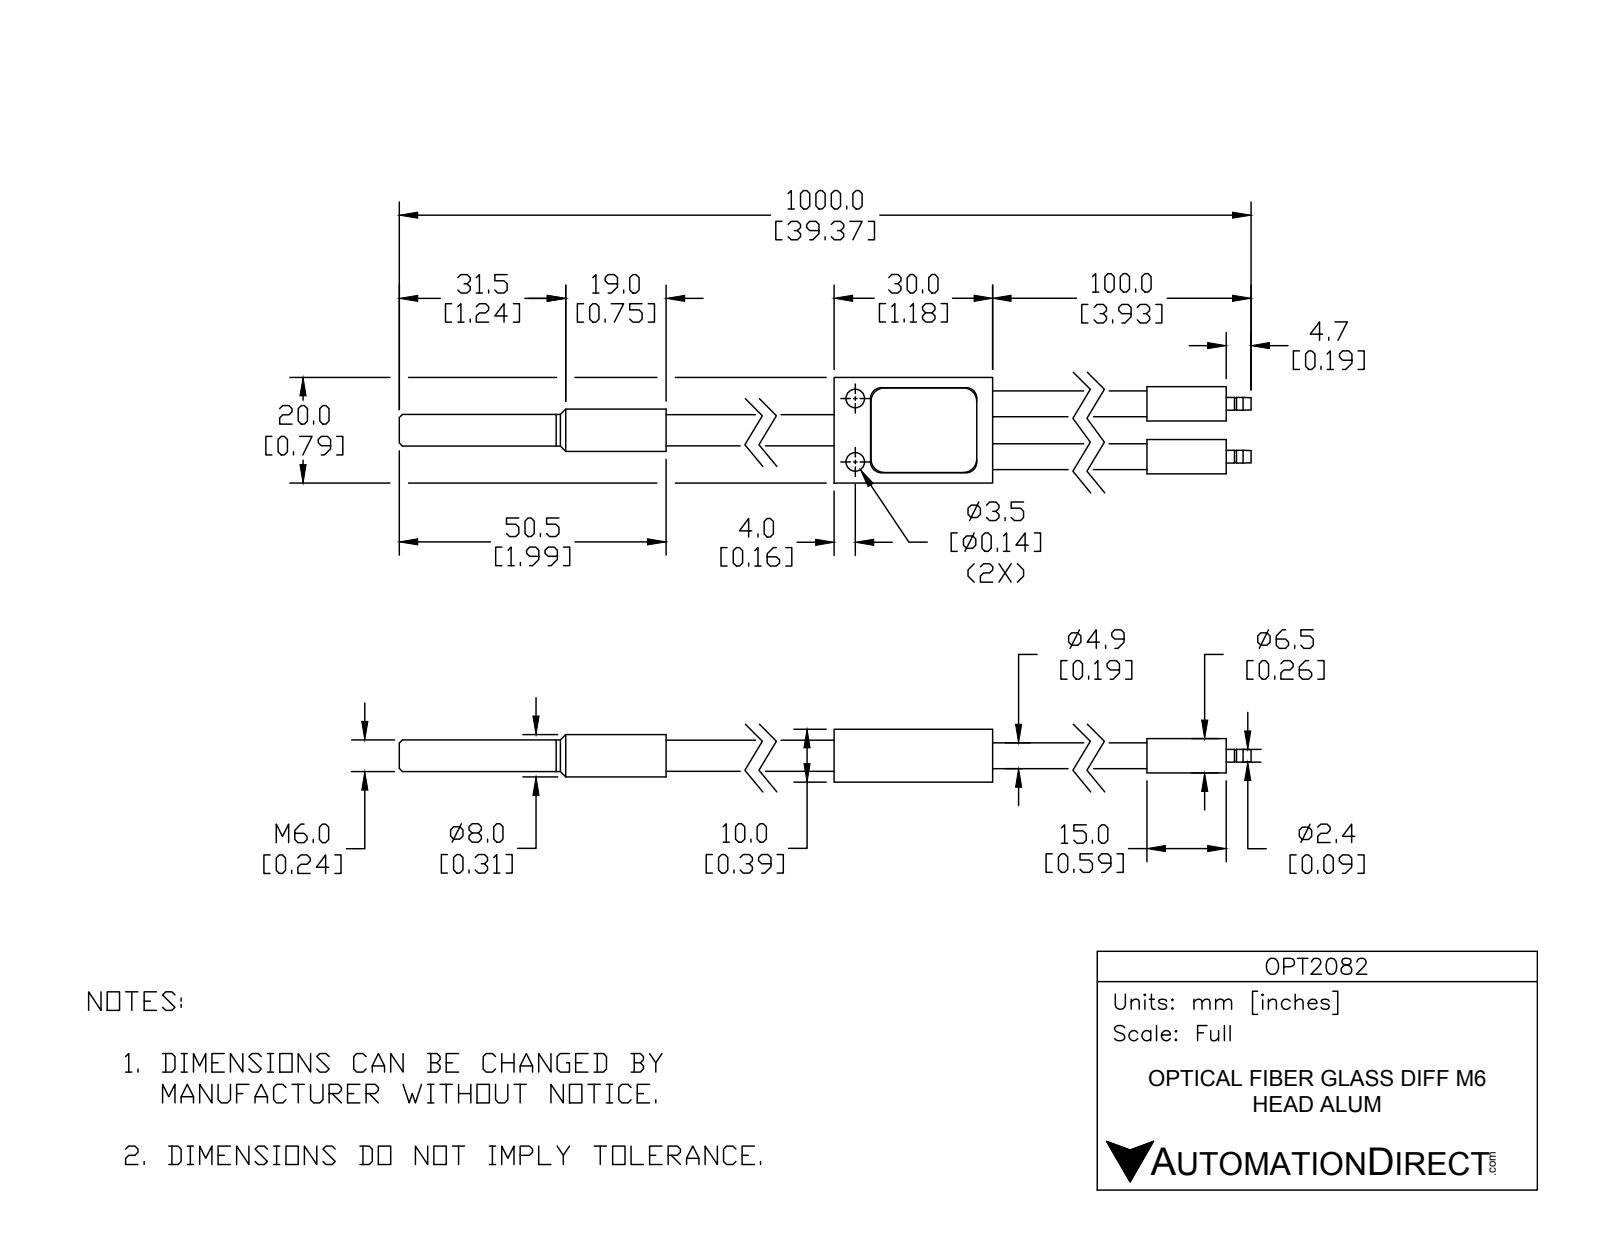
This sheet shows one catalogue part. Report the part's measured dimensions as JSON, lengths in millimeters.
{"part_name": "OPT2082", "step_written_by": "SolidWorks 2014 (AUTOMOTIVE_DESIGN)", "units": "millimeters", "bodies": {"solids": 1, "faces": 73, "planar": 23, "cylindrical": 34, "other": 16}, "overall_size": [1000, 20, 10], "volume_mm3": 34100, "surface_area_mm2": 21910, "round_holes": [[3.5, 2]], "round_bosses_or_shafts": [[6.5, 2], [4.9, 2], [2.4, 2], [8, 1], [6, 1], [5.9, 1]], "partial_cylinders_radius": [[2.5, 4], [2, 2], [2.1, 2]], "face_to_face_distances": [9.9, 20, 10, 30, 125.3, 95.3, 110.3, 80.3, 15, 819.5], "hole_center_spacings": [12]}
